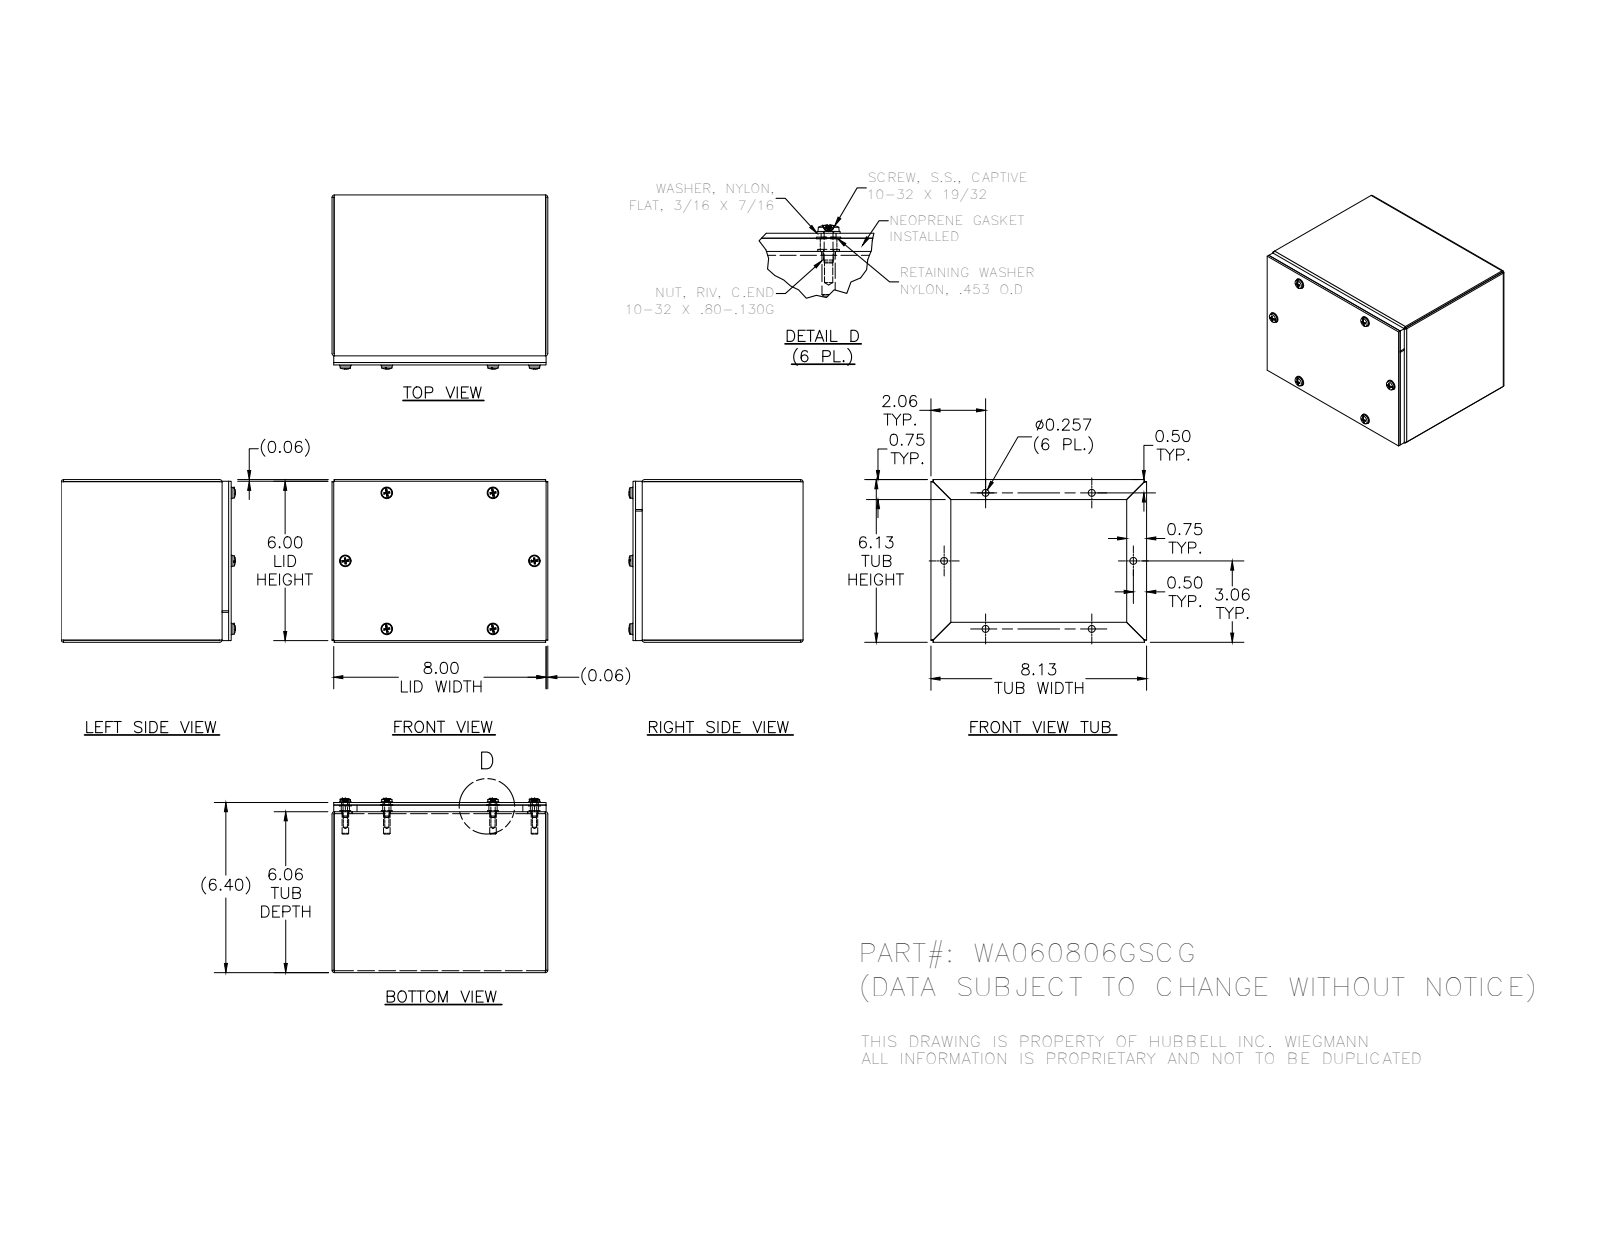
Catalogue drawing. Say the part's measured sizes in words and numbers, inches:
The part is named "34984; 37210; 39077; 39035 (+4 more)". Its 3-D file was written by "SolidWorks 2014 (AUTOMOTIVE_DESIGN)". It is 28 solids with 694 faces: 332 planar, 184 cylindrical and 178 other. Overall it measures 8.125 by 6.558 by 6.125 inches. Its volume is 27.27 cubic inches and its surface area 641.2 square inches. Round holes: 6 of diameter 0.156, 6 of diameter 0.188, 6 of diameter 0.196, 6 of diameter 0.257, 6 of diameter 0.278, 6 of diameter 0.281, 6 of diameter 0.313. Round bosses or shafts: 6 of diameter 0.453, 6 of diameter 0.437, 6 of diameter 0.406, 6 of diameter 0.248, 6 of diameter 0.167. Partial cylindrical surfaces (rounded edges, fillets, slot ends): 8 of radius 0.016, 8 of radius 0.09, 6 of radius 0.089. The main face-to-face distances are 0.074, 6.051, 8.051, 5.986, 0.094, 6.33, 6.404, 6.236, 6.31, 6.125. The hole center spacings are 4, 3.001, 6.124, 3.001, 6.124, 3, 5.124, 6.124.
